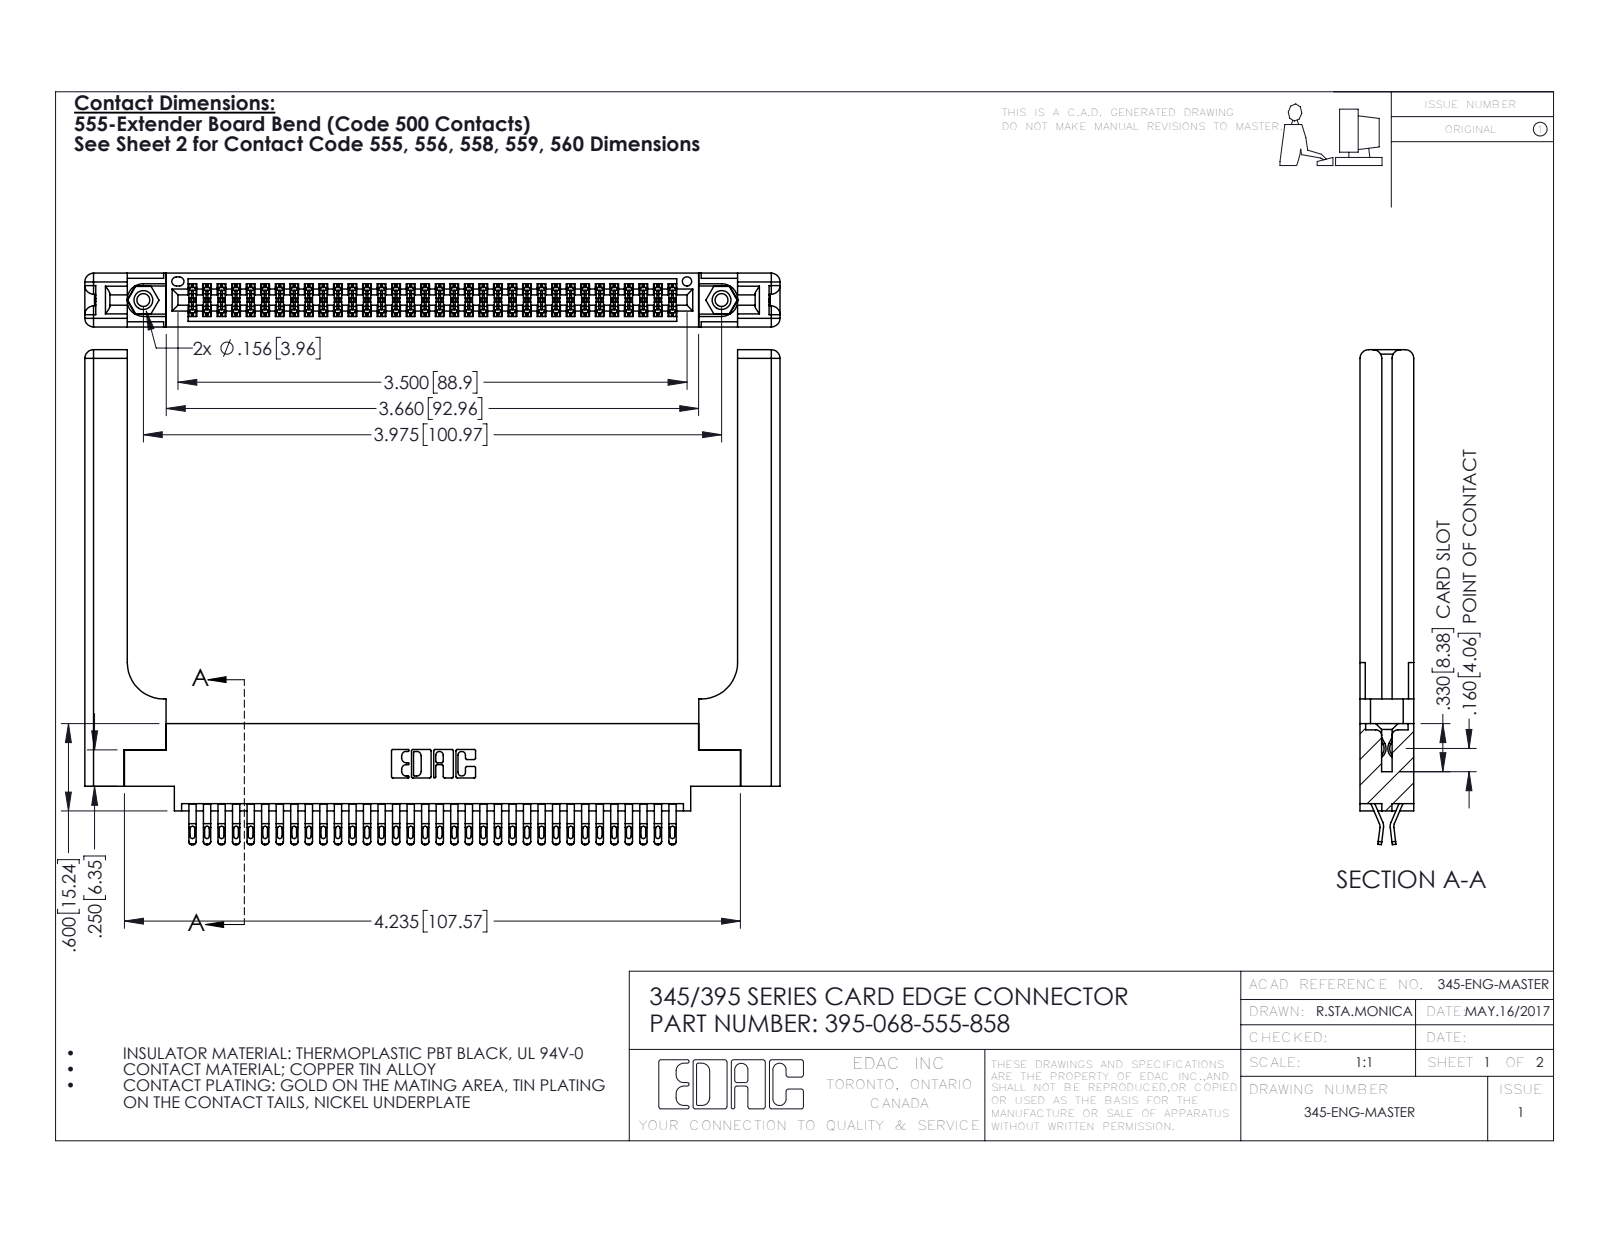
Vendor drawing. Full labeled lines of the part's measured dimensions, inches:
Part name (STEP PRODUCT): 345-220-058_345-220-058; 395-068-555-858; 345-250-001_345-250-001-102; 345-292-001_555 Tail (+1 more)
STEP written by: SolidWorks 2016 (CONFIG_CONTROL_DESIGN)
Units: inches
Bodies: 73 solids, 4194 faces (2340 planar, 1794 cylindrical, 60 other)
Overall size (bounding box): 4.779 × 3.402 × 0.37
Volume: 1.237 in³ · Surface area: 35.93 in²
Round holes (diameter × count): ⌀0.089 ×2, ⌀0.125 ×2, ⌀0.156 ×2, ⌀0.064 ×1
Round bosses / shafts (diameter × count): ⌀0.155 ×2
Partial cylindrical surfaces — rounded edges, fillets, slot ends (radius × count): R0.016 ×170, R0.02 ×136, R0.006 ×102, R0.01 ×22, R0.06 ×16, R0.007 ×6, R0.031 ×6, R0.026 ×3
Main face-to-face distances: 0.37, 0.072, 0.298, 0.025, 0.098, 0.272, 0.2, 0.225, 0.148, 0.15
Hole centre spacings: 0.27, 3.74, 3.975
